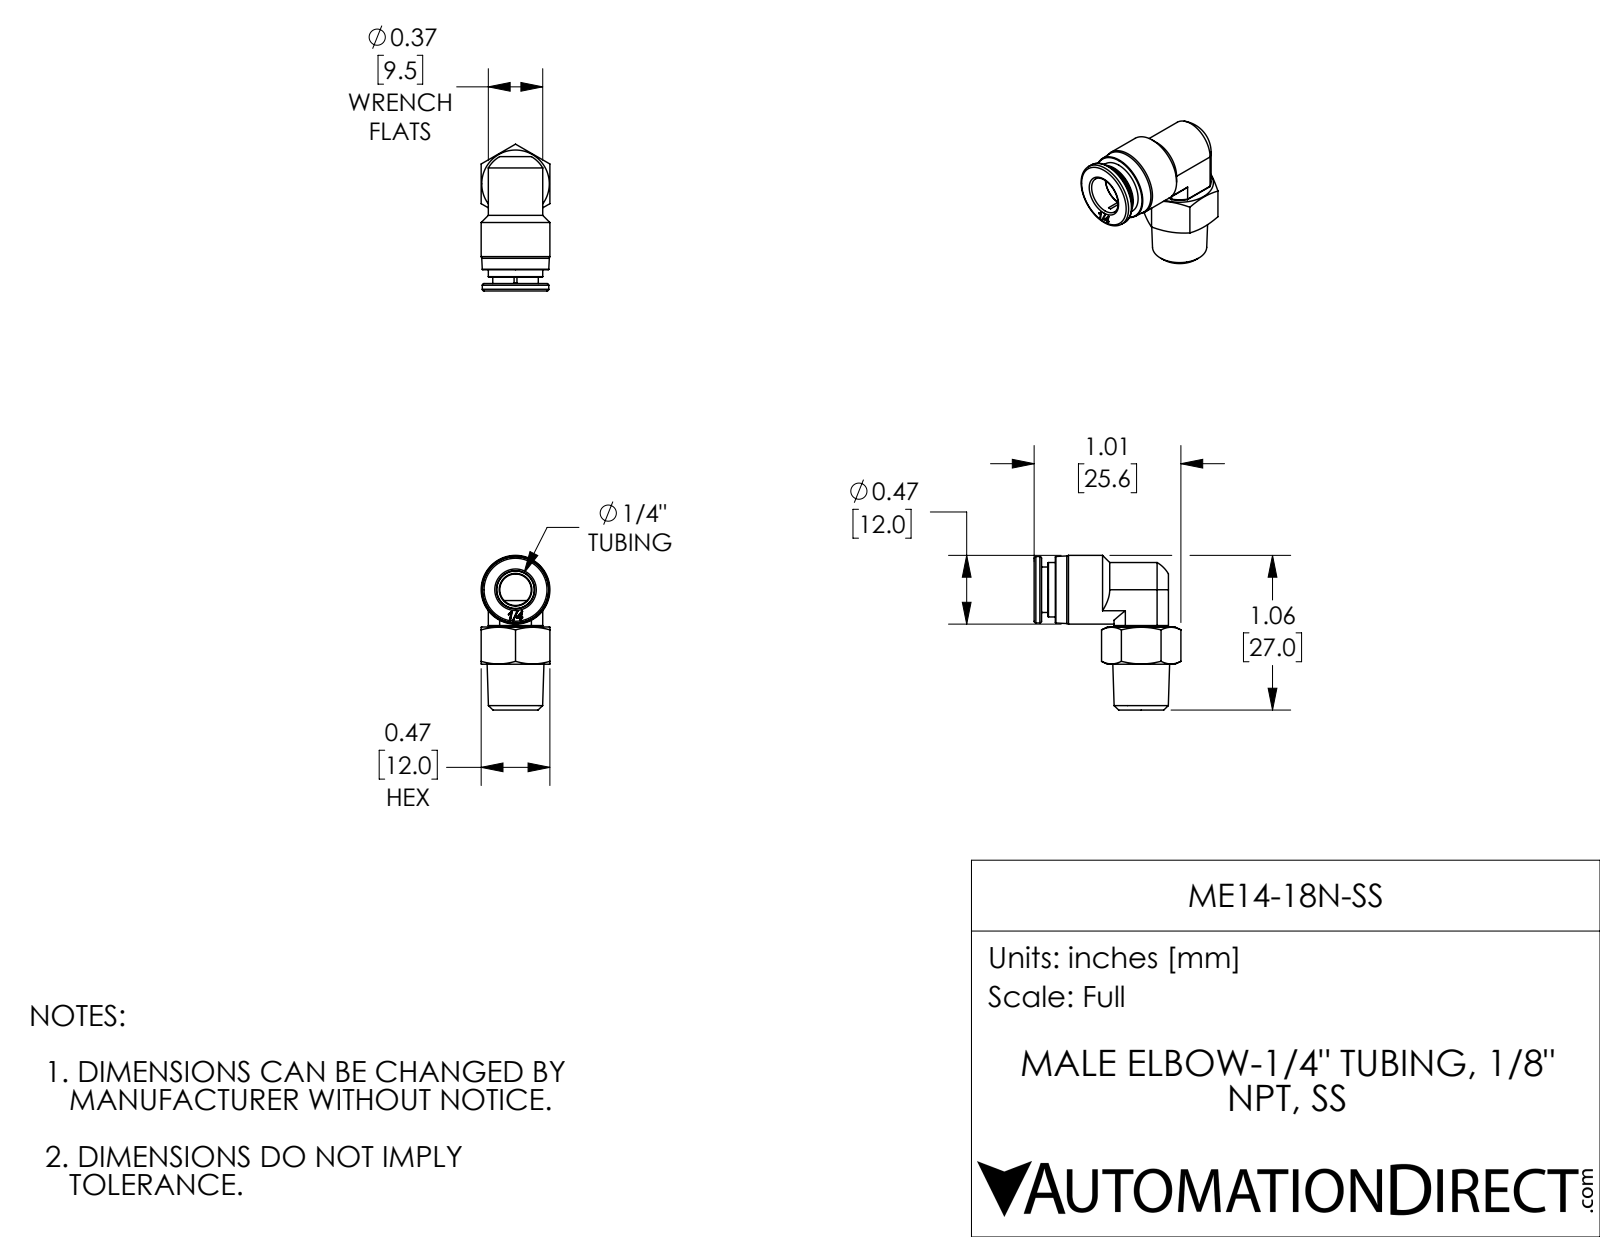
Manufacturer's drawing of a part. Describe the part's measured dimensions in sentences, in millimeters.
The part is named "ME14-18N-SS". Its 3-D file was written by "SolidWorks 2017 (AUTOMOTIVE_DESIGN)". It is 2 solids with 134 faces: 55 planar, 33 cylindrical and 46 other. Overall it measures 27 by 25.6 by 12 millimeters. Its volume is 2 750 cubic millimeters and its surface area 2 775 square millimeters. Round holes: 1 of diameter 4, 1 of diameter 5.5, 1 of diameter 6, 1 of diameter 6.6, 1 of diameter 6.7, 1 of diameter 8.1. Round bosses or shafts: 1 of diameter 12, 1 of diameter 11.6, 1 of diameter 9.5, 1 of diameter 8, 1 of diameter 6. Partial cylindrical surfaces (rounded edges, fillets, slot ends): 4 of radius 0.2, 1 of radius 5.5. The main face-to-face distances are 12, 1.2, 10.7, 1.3, 9.5, 23.4, 22.1, 2.4, 14.5, 3.7.
